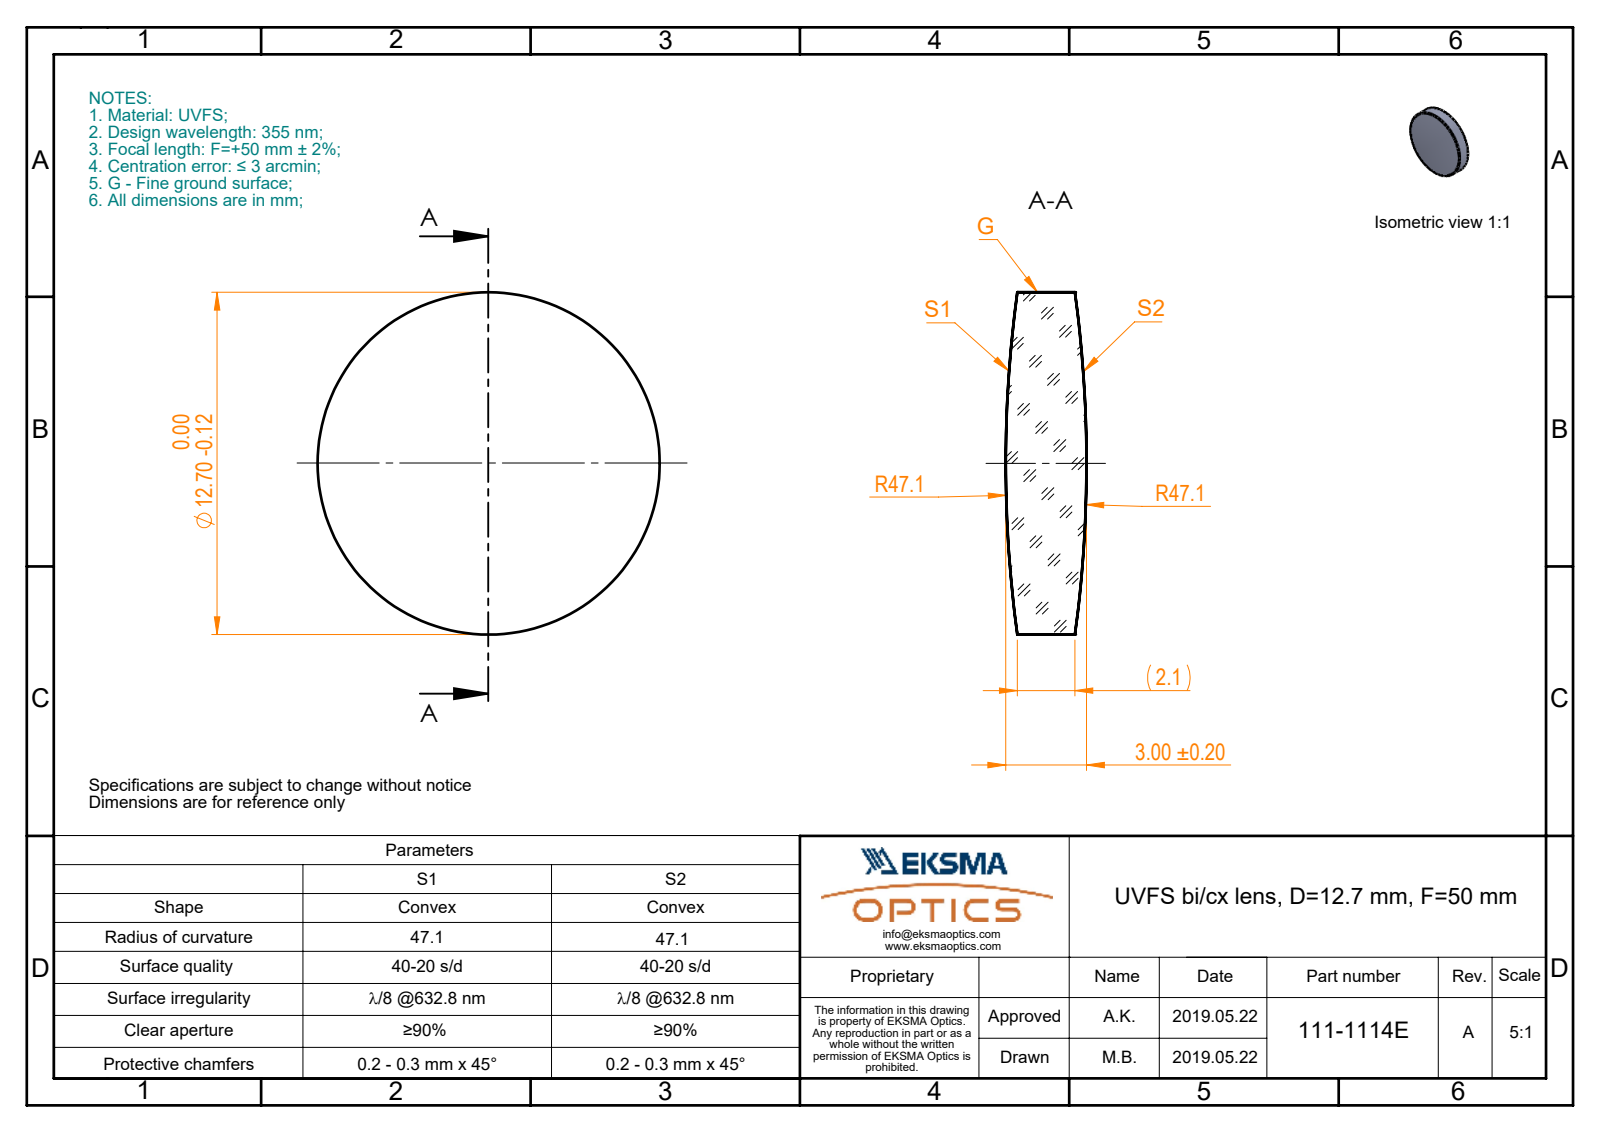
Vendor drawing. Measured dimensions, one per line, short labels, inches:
name: 111-1114E UVFS bi-cx 12.7 F50
written by: SolidWorks 2017 (CONFIG_CONTROL_DESIGN)
unit: in
bodies: 1 solid, 6 faces (0 planar, 2 cylindrical, 4 other)
size: 0.5 × 0.5 × 0.118
volume: 0.02 in³; area: 0.527 in²
bosses: 1× ⌀0.5
